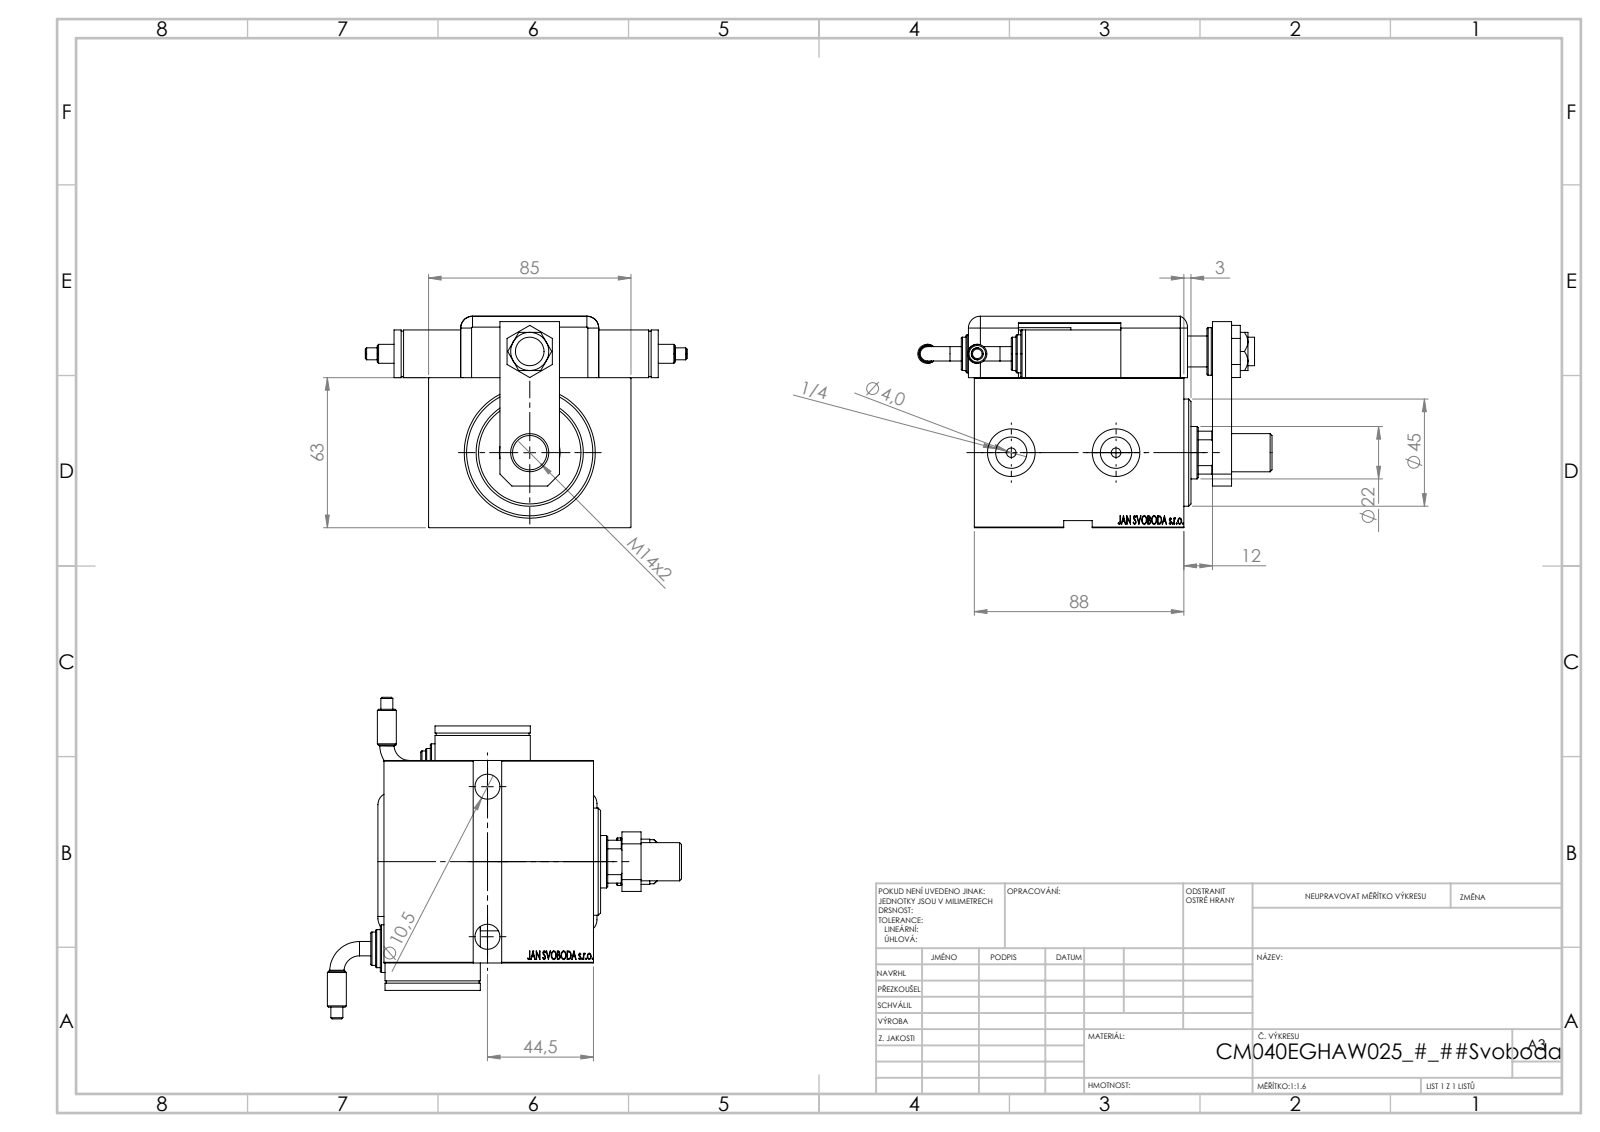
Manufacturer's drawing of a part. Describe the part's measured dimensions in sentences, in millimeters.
The part is named "KRYT; SWITCH DIM A_G; MAGNETIC SWITCH Q; V450CM_MALE_METRIC (+7 more)". Its 3-D file was written by "SolidWorks 2019 (CONFIG_CONTROL_DESIGN)". It is 14 solids with 1272 faces: 622 planar, 111 cylindrical and 539 other. Overall it measures 148.76 by 135.01 by 88.8 millimeters. Its volume is 578 365 cubic millimeters and its surface area 124 990 square millimeters. Round holes: 4 of diameter 4, 2 of diameter 8, 2 of diameter 10.5, 2 of diameter 13.16, 2 of diameter 14, 2 of diameter 16.5, 2 of diameter 20, 1 of diameter 12, 1 of diameter 12.5, 1 of diameter 13, 1 of diameter 22, 1 of diameter 25.5. Round bosses or shafts: 3 of diameter 20, 3 of diameter 16, 3 of diameter 14, 2 of diameter 8, 2 of diameter 6, 2 of diameter 5.04, 1 of diameter 45, 1 of diameter 42. Partial cylindrical surfaces (rounded edges, fillets, slot ends): 9 of radius 5, 1 of radius 10, 1 of radius 10.5. The main face-to-face distances are 3, 83, 63, 88, 85, 13.5, 12, 20, 1.5, 88.8. The hole center spacings are 41.5, 54.61, 1, 20, 42.5, 43.5, 44, 63.
